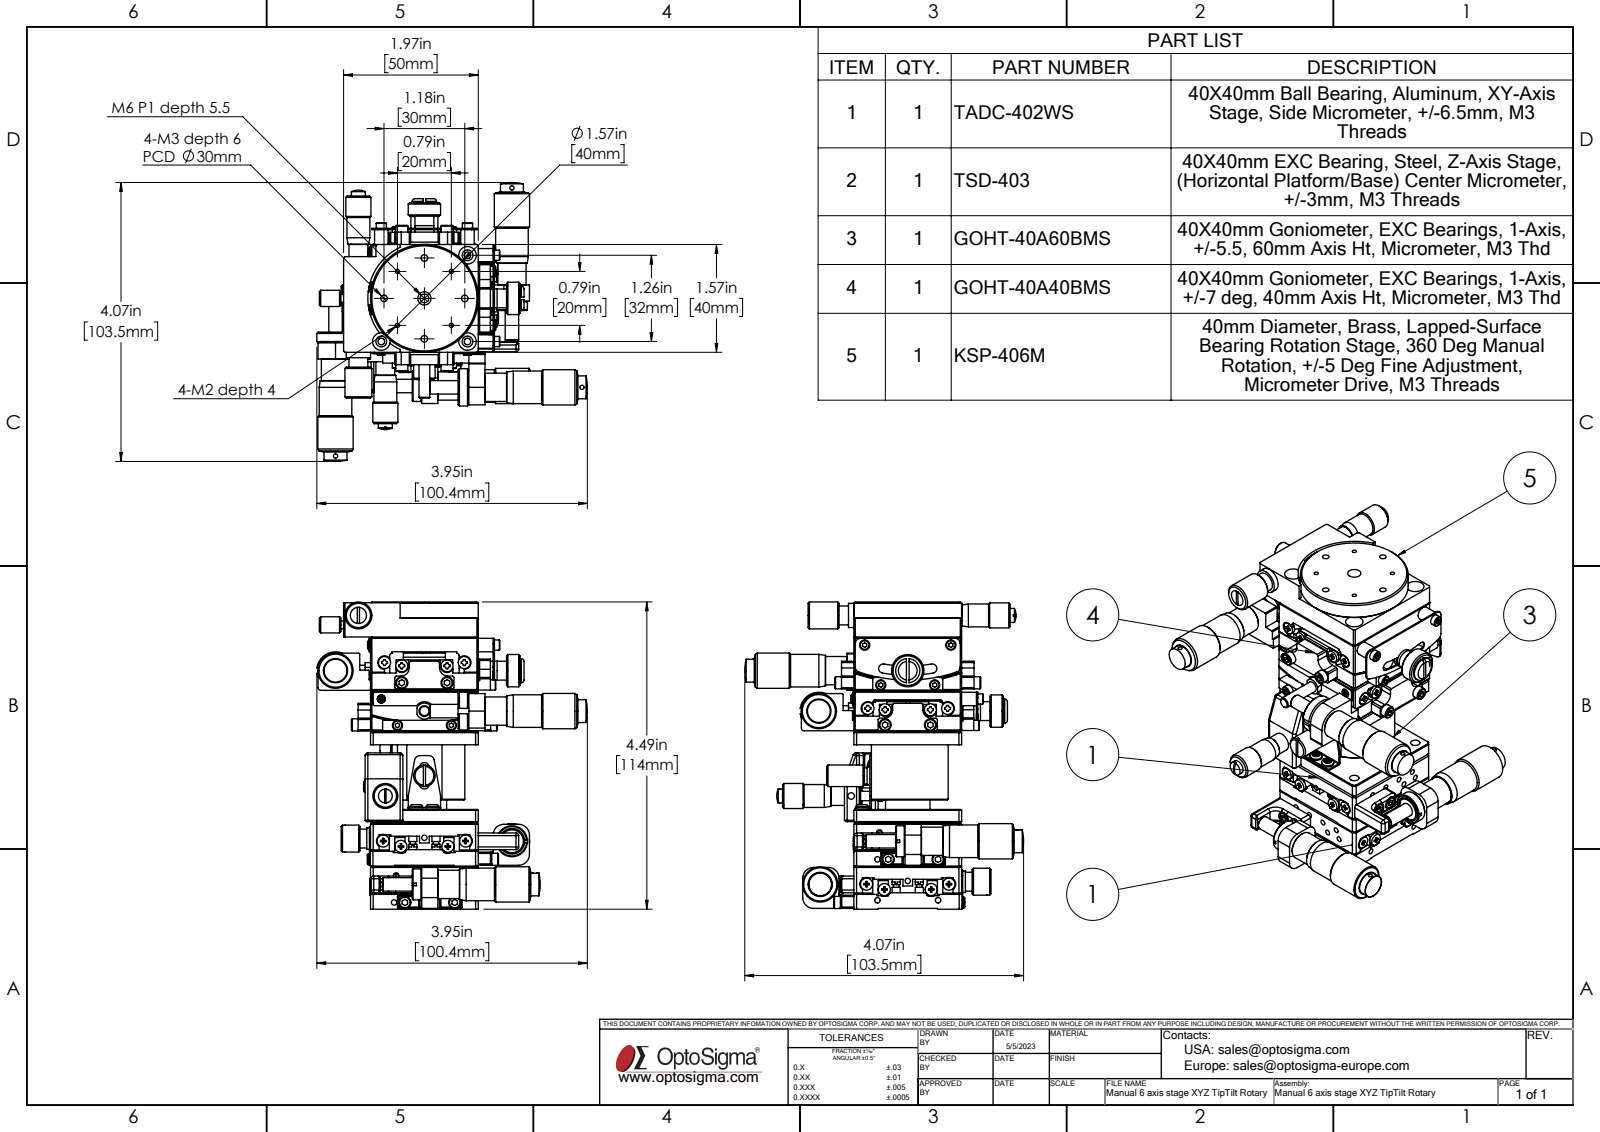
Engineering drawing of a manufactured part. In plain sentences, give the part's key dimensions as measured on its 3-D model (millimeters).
The part is named "GOHT-40A60BMS; TSD-403; Manual 6 axis stage XYZ TipTilt Rotary; KSP-406M (+8 more)". Its 3-D file was written by "SolidWorks 2023 (AUTOMOTIVE_DESIGN)". It is 22 solids with 6804 faces: 2877 planar, 2088 cylindrical and 1839 other. Overall it measures 114 by 103.5 by 100.43 millimeters. Its volume is 133 761 cubic millimeters and its surface area 124 825 square millimeters. Round holes: 44 of diameter 1.57, 36 of diameter 2.5, 36 of diameter 4.3, 32 of diameter 2.2, 26 of diameter 2.1, 20 of diameter 2.01, 18 of diameter 2, 14 of diameter 1.57, 12 of diameter 2.01, 11 of diameter 3, 8 of diameter 5, 7 of diameter 2.46. Round bosses or shafts: 49 of diameter 2, 48 of diameter 3.8, 37 of diameter 4.5, 21 of diameter 3, 16 of diameter 2.5, 9 of diameter 5, 9 of diameter 4, 8 of diameter 1.5. Partial cylindrical surfaces (rounded edges, fillets, slot ends): 49 of radius 1, 40 of radius 0.8, 34 of radius 0.5, 19 of radius 2, 18 of radius 3, 16 of radius 2.5, 11 of radius 4, 5 of radius 1.5. The main face-to-face distances are 40, 16, 15, 5, 7, 33, 69, 20, 24, 9.9. The hole center spacings are 7.5, 30.22, 24.08, 3.5, 4, 7, 11, 13.36.
